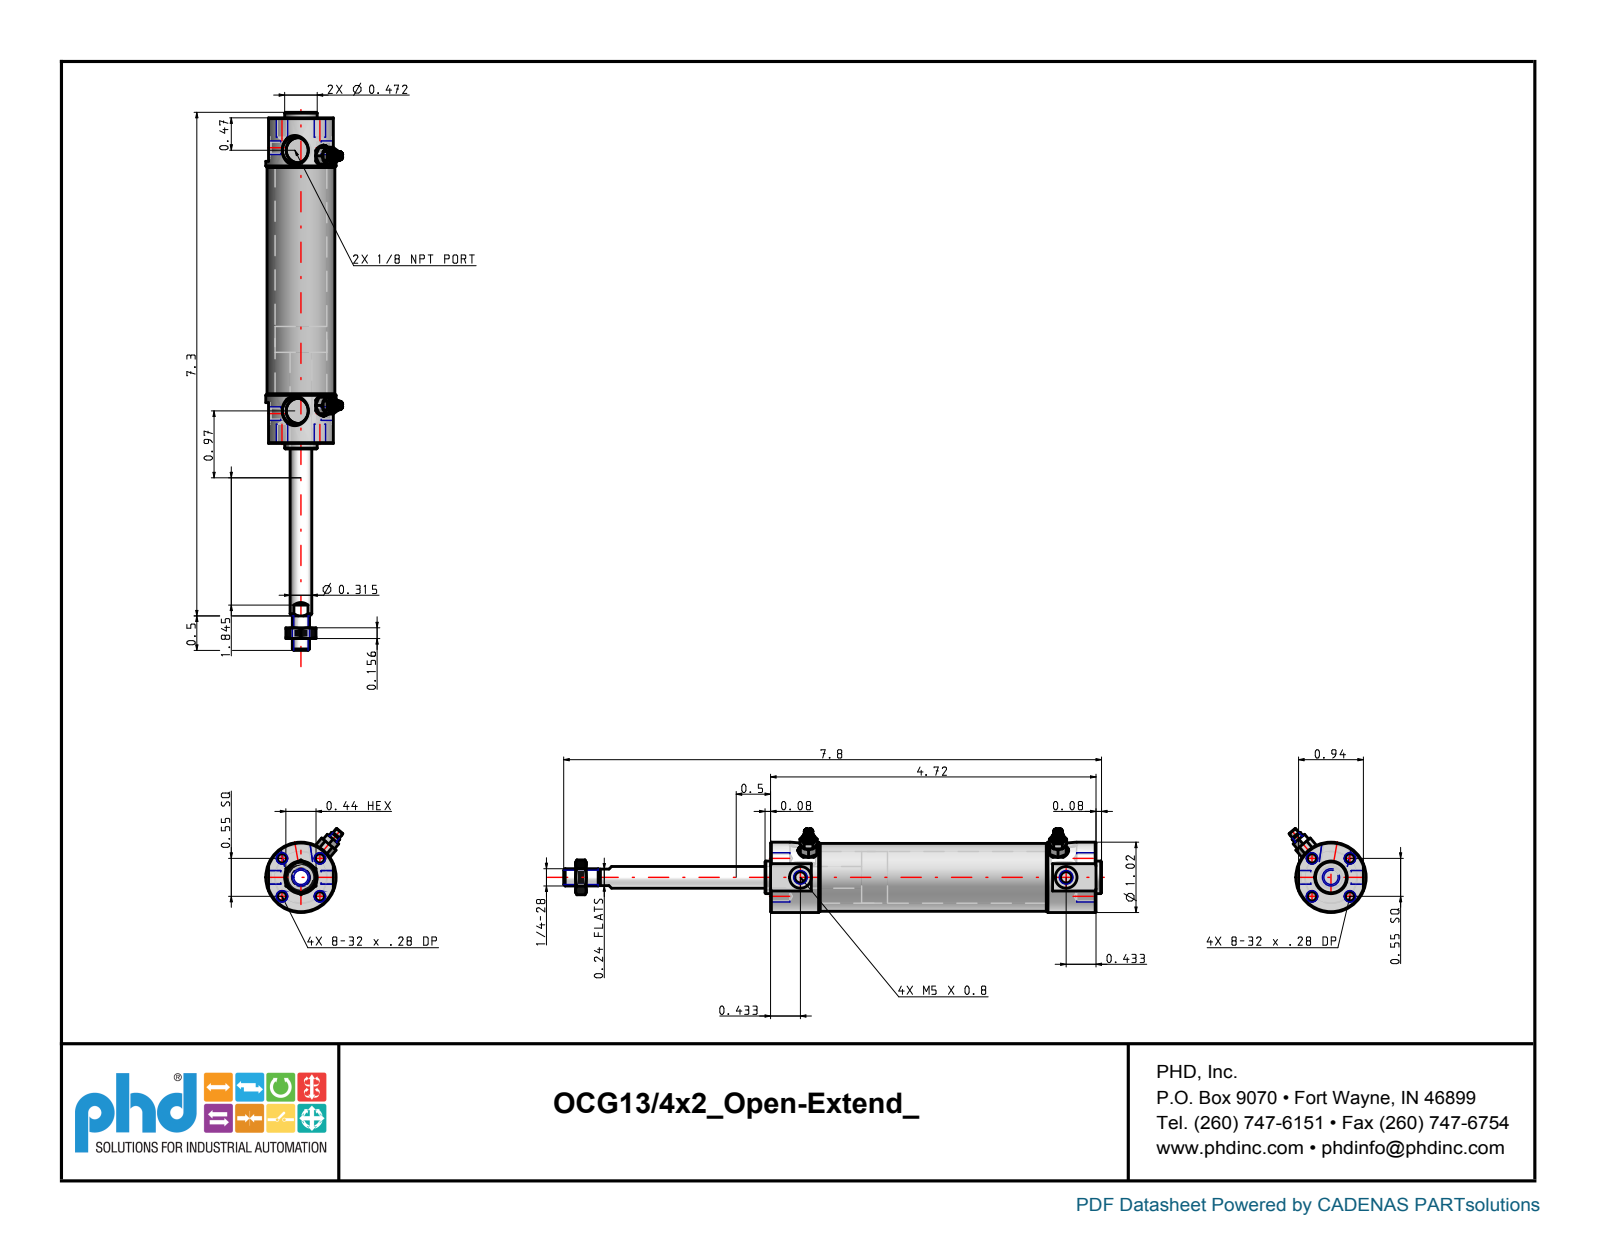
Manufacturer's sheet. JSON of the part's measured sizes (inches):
{"part_name": "OCG13/4x2_Open-Extend; TUBE_OCG13/4x2_Open-Extend; HD_OCG13/4x2_Open-Extend; PR_OCG1-3/4x2 (+2 more)", "step_written_by": "PARTsolutions (CONFIG_CONTROL_DESIGN)", "units": "inches", "bodies": {"solids": 5, "faces": 204, "planar": 111, "cylindrical": 35, "other": 58}, "overall_size": [7.8, 1.217, 1.116], "volume_in3": 2.553, "surface_area_in2": 36.19, "round_holes": [[0.134, 4], [0.163, 2], [0.315, 2], [0.211, 1], [0.316, 1], [0.75, 1]], "round_bosses_or_shafts": [[0.157, 2], [0.124, 2], [1.02, 1], [0.984, 1], [0.749, 1], [0.472, 1], [0.315, 1], [0.25, 1]], "partial_cylinders_radius": [[0.154, 2]], "face_to_face_distances": [0.709, 4.011, 3.302, 4.72, 3.024, 2.315, 0.987, 1.696, 3.399, 2.691], "hole_center_spacings": [0.389, 0.55, 0.778, 3.854]}
